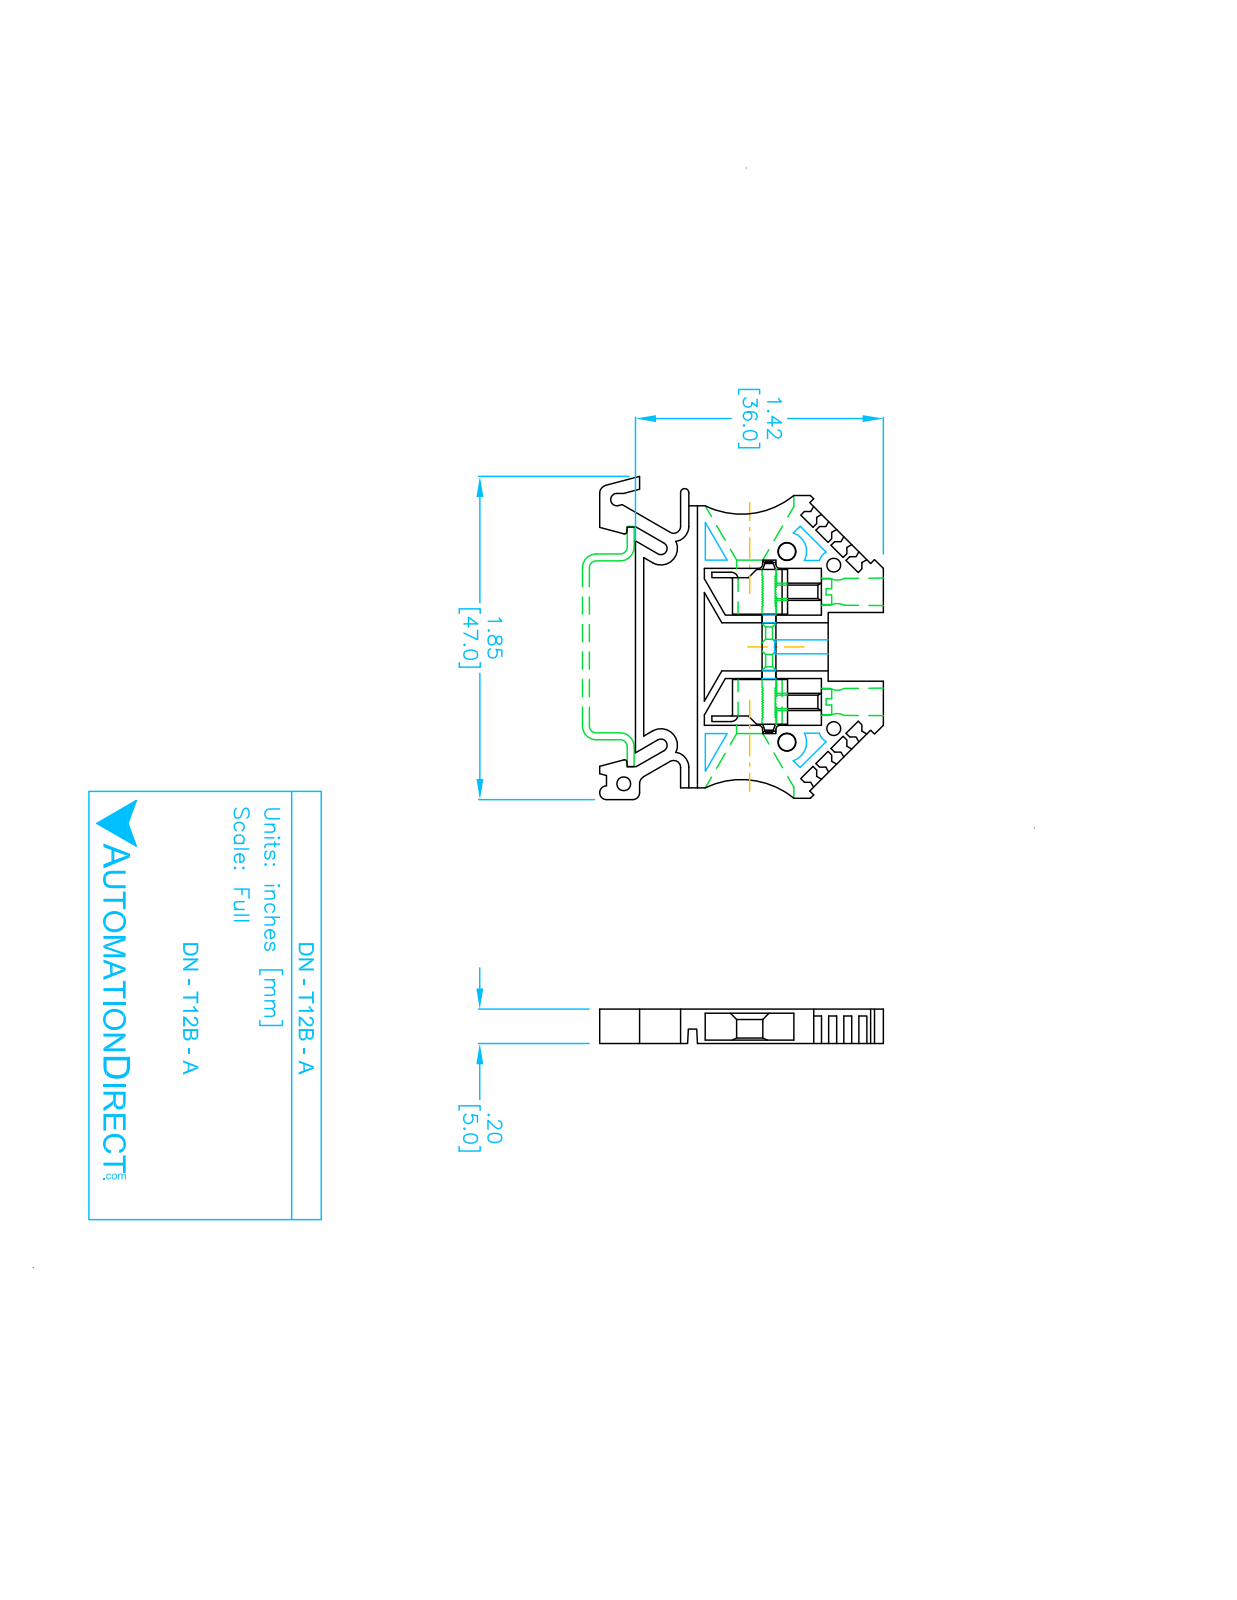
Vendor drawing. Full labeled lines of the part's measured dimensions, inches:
Part name (STEP PRODUCT): DN-T12B-A
STEP written by: SolidWorks 2017 (AUTOMOTIVE_DESIGN)
Units: inches
Bodies: 1 solid, 169 faces (134 planar, 35 cylindrical, 0 other)
Overall size (bounding box): 1.85 × 1.622 × 0.197
Volume: 0.306 in³ · Surface area: 7.131 in²
Round holes (diameter × count): ⌀0.164 ×2, ⌀0.079 ×1
Partial cylindrical surfaces — rounded edges, fillets, slot ends (radius × count): R0.039 ×4, R0.035 ×3, R0.012 ×2, R0.047 ×2, R0.087 ×2, R0.094 ×2, R0.472 ×2, R0.024 ×1
Main face-to-face distances: 0.189, 0.197, 0.087, 0.02, 0.106, 0.094, 0.114, 0.083, 0.102, 0.354
Hole centre spacings: 0.589
